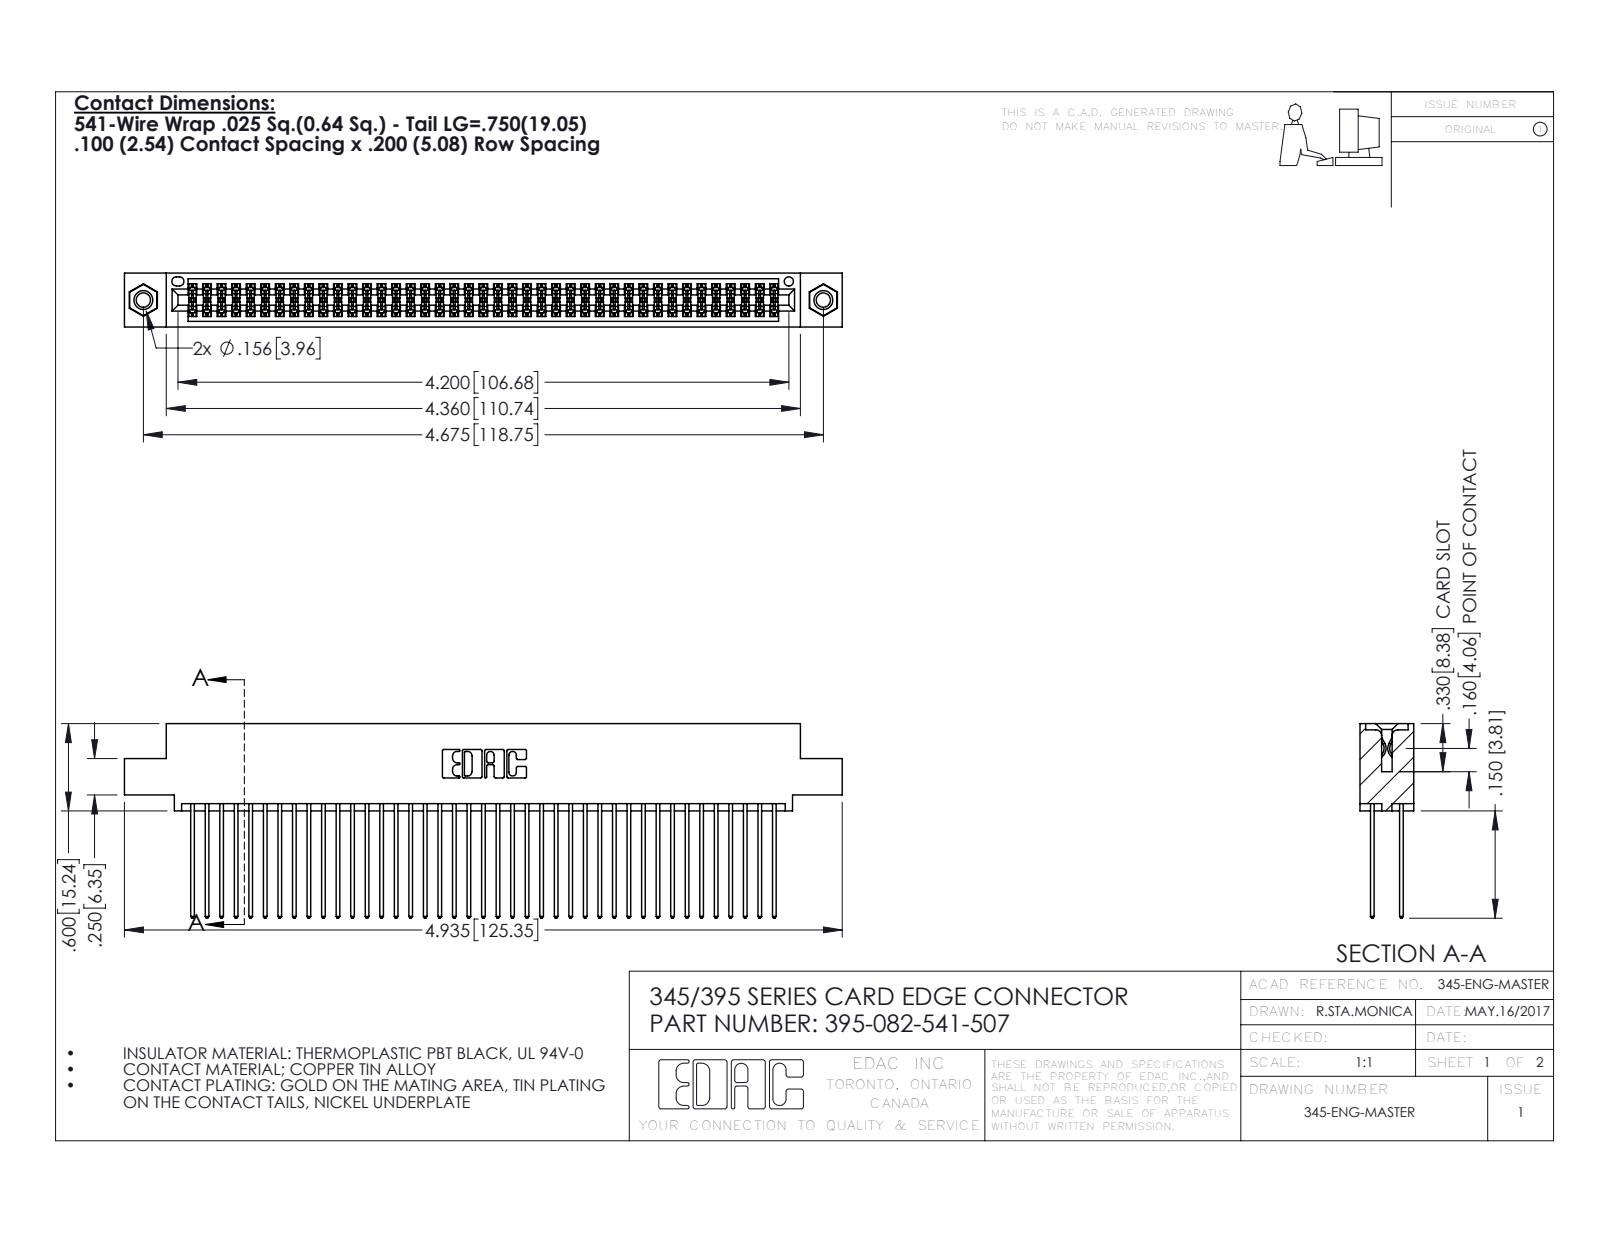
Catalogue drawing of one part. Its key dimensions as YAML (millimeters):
part_name: "345-292-001_345-293-141; 345-250-001_345-250-005-103; 345 Part_0.110 Offset - 0.156 Dia-TI; 395-082-541-507"
step_written_by: "SolidWorks 2016 (CONFIG_CONTROL_DESIGN)"
units: millimeters
bodies: {solids: 85, faces: 4290, planar: 2822, cylindrical: 1452, other: 16}
overall_size: [125.3, 34, 9.4]
volume: 12600
surface_area: 20860
round_holes:
  - {diameter: 2.5, count: 2}
  - {diameter: 3.2, count: 2}
  - {diameter: 4, count: 2}
  - {diameter: 1.6, count: 1}
round_bosses_or_shafts:
  - {diameter: 3.9, count: 2}
partial_cylinders:
  - {radius: 0.2, count: 123}
  - {radius: 0.3, count: 82}
  - {radius: 0.3, count: 22}
  - {radius: 0.2, count: 6}
  - {radius: 0.8, count: 6}
  - {radius: 0.7, count: 3}
  - {radius: 0.4, count: 2}
  - {radius: 0.5, count: 2}
face_to_face_distances: [1.8, 7.6, 5.1, 2.5, 6.9, 0.6, 5.7, 9.4, 4.4, 3.8]
hole_center_spacings: [6.9, 112.8, 118.7]
